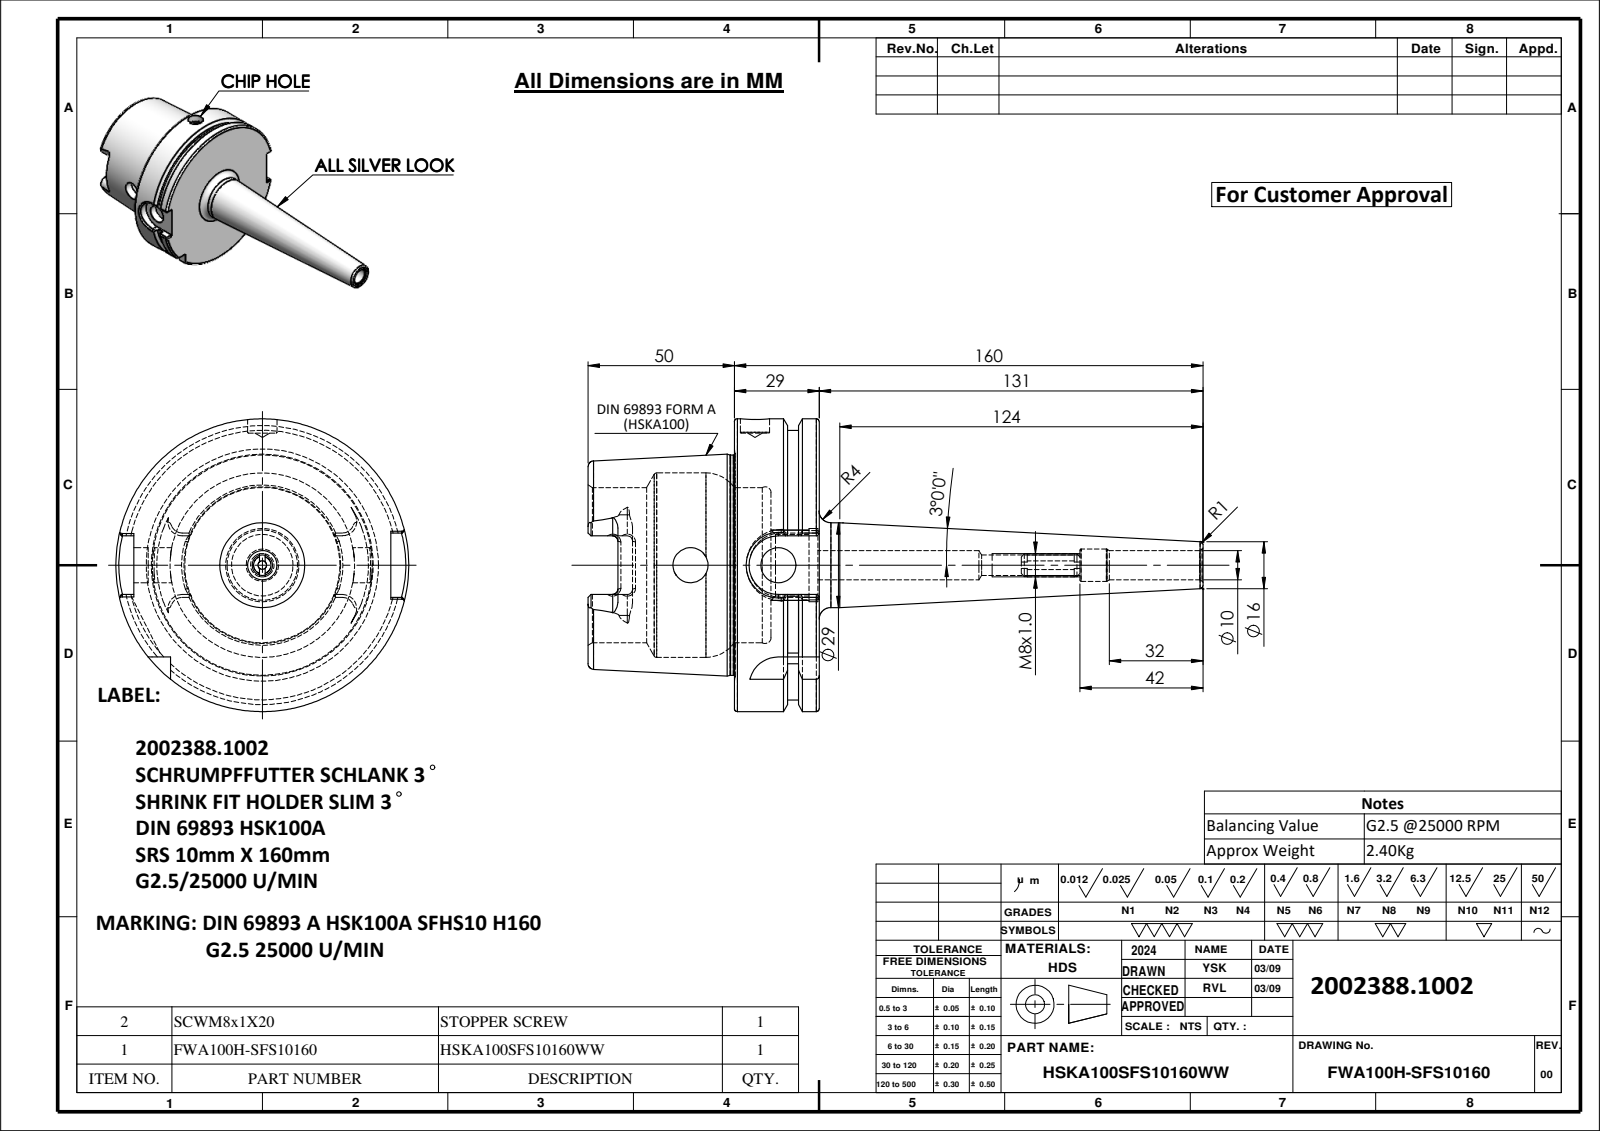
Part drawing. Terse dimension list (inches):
name: SCWM8X1; FWA100H-SFS10160; HSKA100SFS10160WW
written by: SolidWorks 2024 (CONFIG_CONTROL_DESIGN)
unit: in
bodies: 2 solids, 210 faces (68 planar, 58 cylindrical, 84 other)
size: 8.268 × 3.937 × 3.937
volume: 18.37 in³; area: 97.94 in²
holes: 2× ⌀0.394, 2× ⌀0.472, 1× ⌀0.118, 1× ⌀0.276, 1× ⌀0.433, 1× ⌀0.827, 1× ⌀0.984, 1× ⌀2.087, 1× ⌀2.48
bosses: 1× ⌀3.937, 1× ⌀3.622, 1× ⌀2.959, 1× ⌀1.142, 1× ⌀0.315
rounds: 6× R0.071, 4× R0.192, 2× R0.394, 1× R0.433
face distances: 1.14, 0.492, 0.648, 1.969, 2.461, 3.108, 0.63, 3.091, 1.122, 0.018
hole spacings: 1.181
